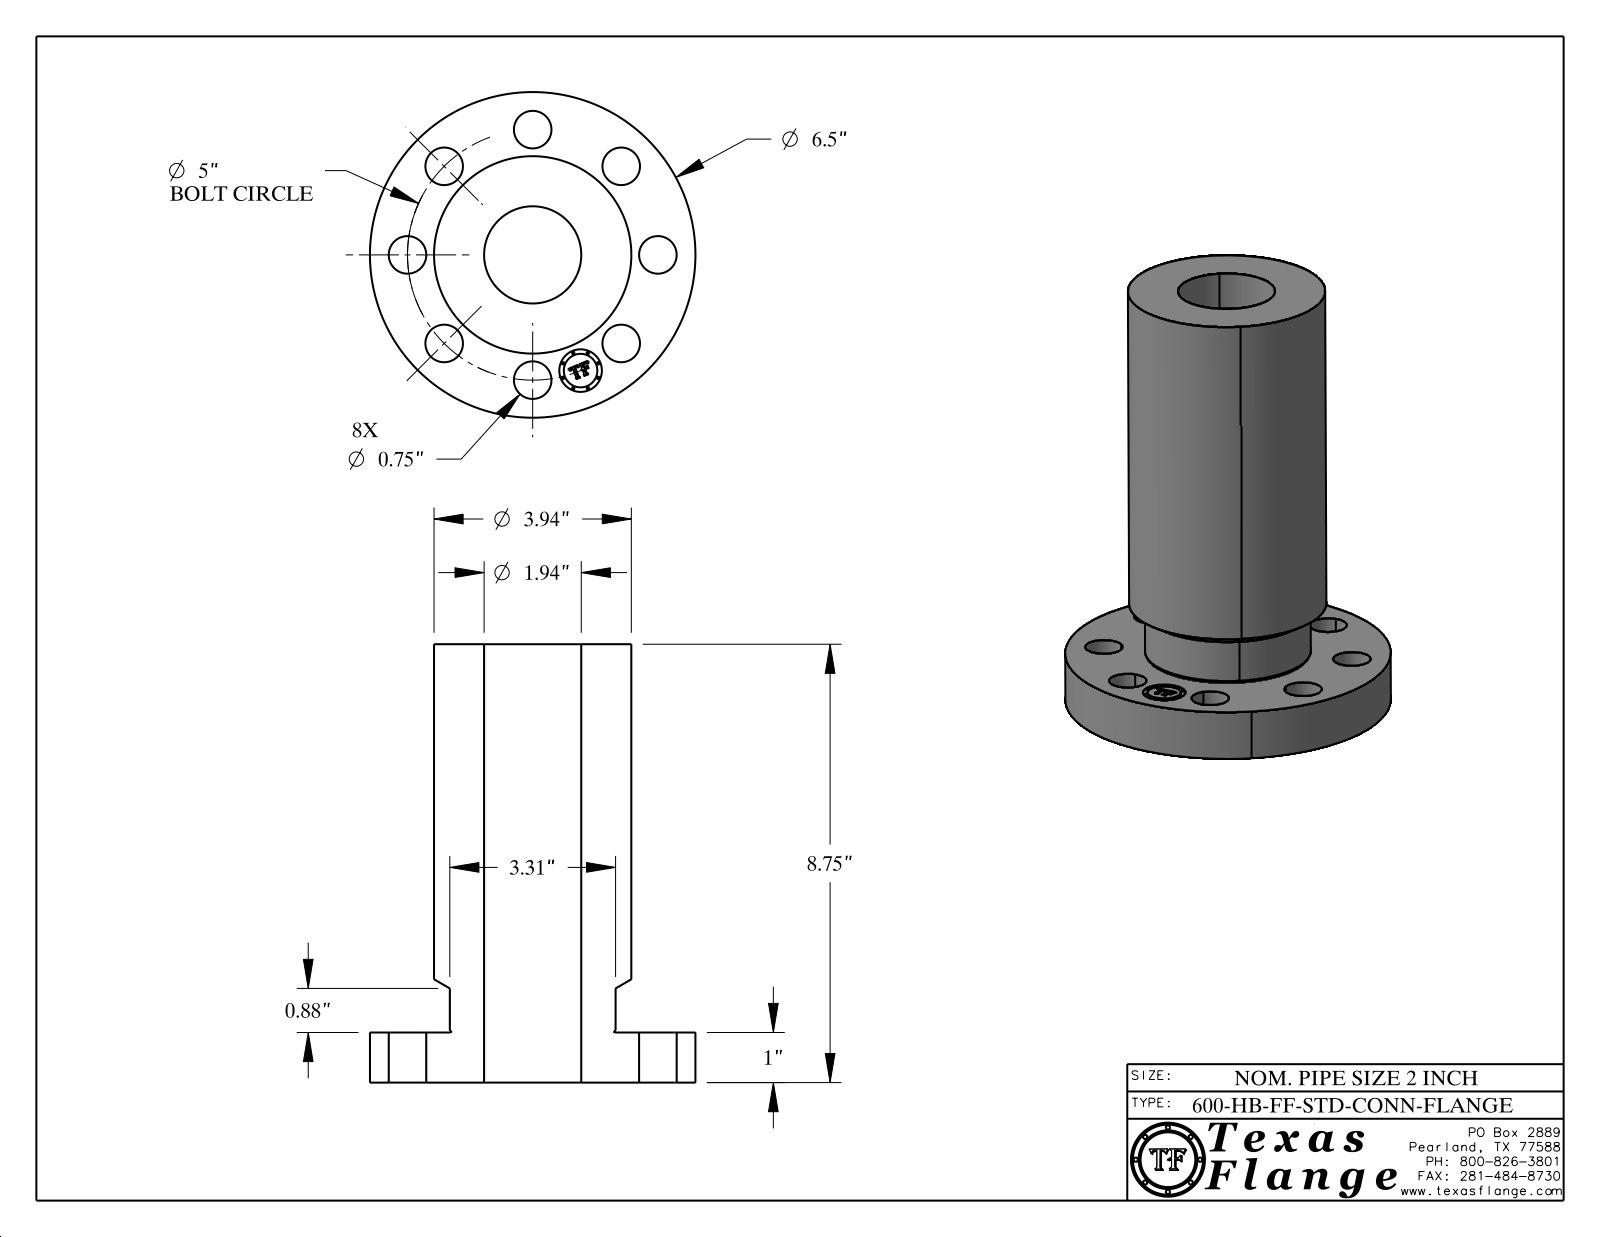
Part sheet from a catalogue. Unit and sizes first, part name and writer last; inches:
Units: inches
Overall size (bounding box): 8.75 × 6.5 × 6.5
Round holes (diameter × count): ⌀0.75 ×8, ⌀0.85 ×1, ⌀1.94 ×1
Round bosses / shafts (diameter × count): ⌀0.051 ×8, ⌀6.5 ×1, ⌀3.94 ×1, ⌀3.31 ×1, ⌀0.67 ×1
Main face-to-face distances: 1, 8.75, 7.75, 0.995, 7.755, 0.254, 0.249, 0.046, 0.164, 0.211
Hole centre spacings: 2.5, 1.913, 3.535, 4.619, 5, 0.976, 2.778, 4.157
Volume: 94.77 in³ · Surface area: 246.1 in²
Bodies: 1 solid, 418 faces (368 planar, 44 cylindrical, 6 other)
Part name (STEP PRODUCT): 2-600-HB-FF-STD-CONN-FLANGE
STEP written by: CATIA V5 STEP AP214 (AUTOMOTIVE_DESIGN)
